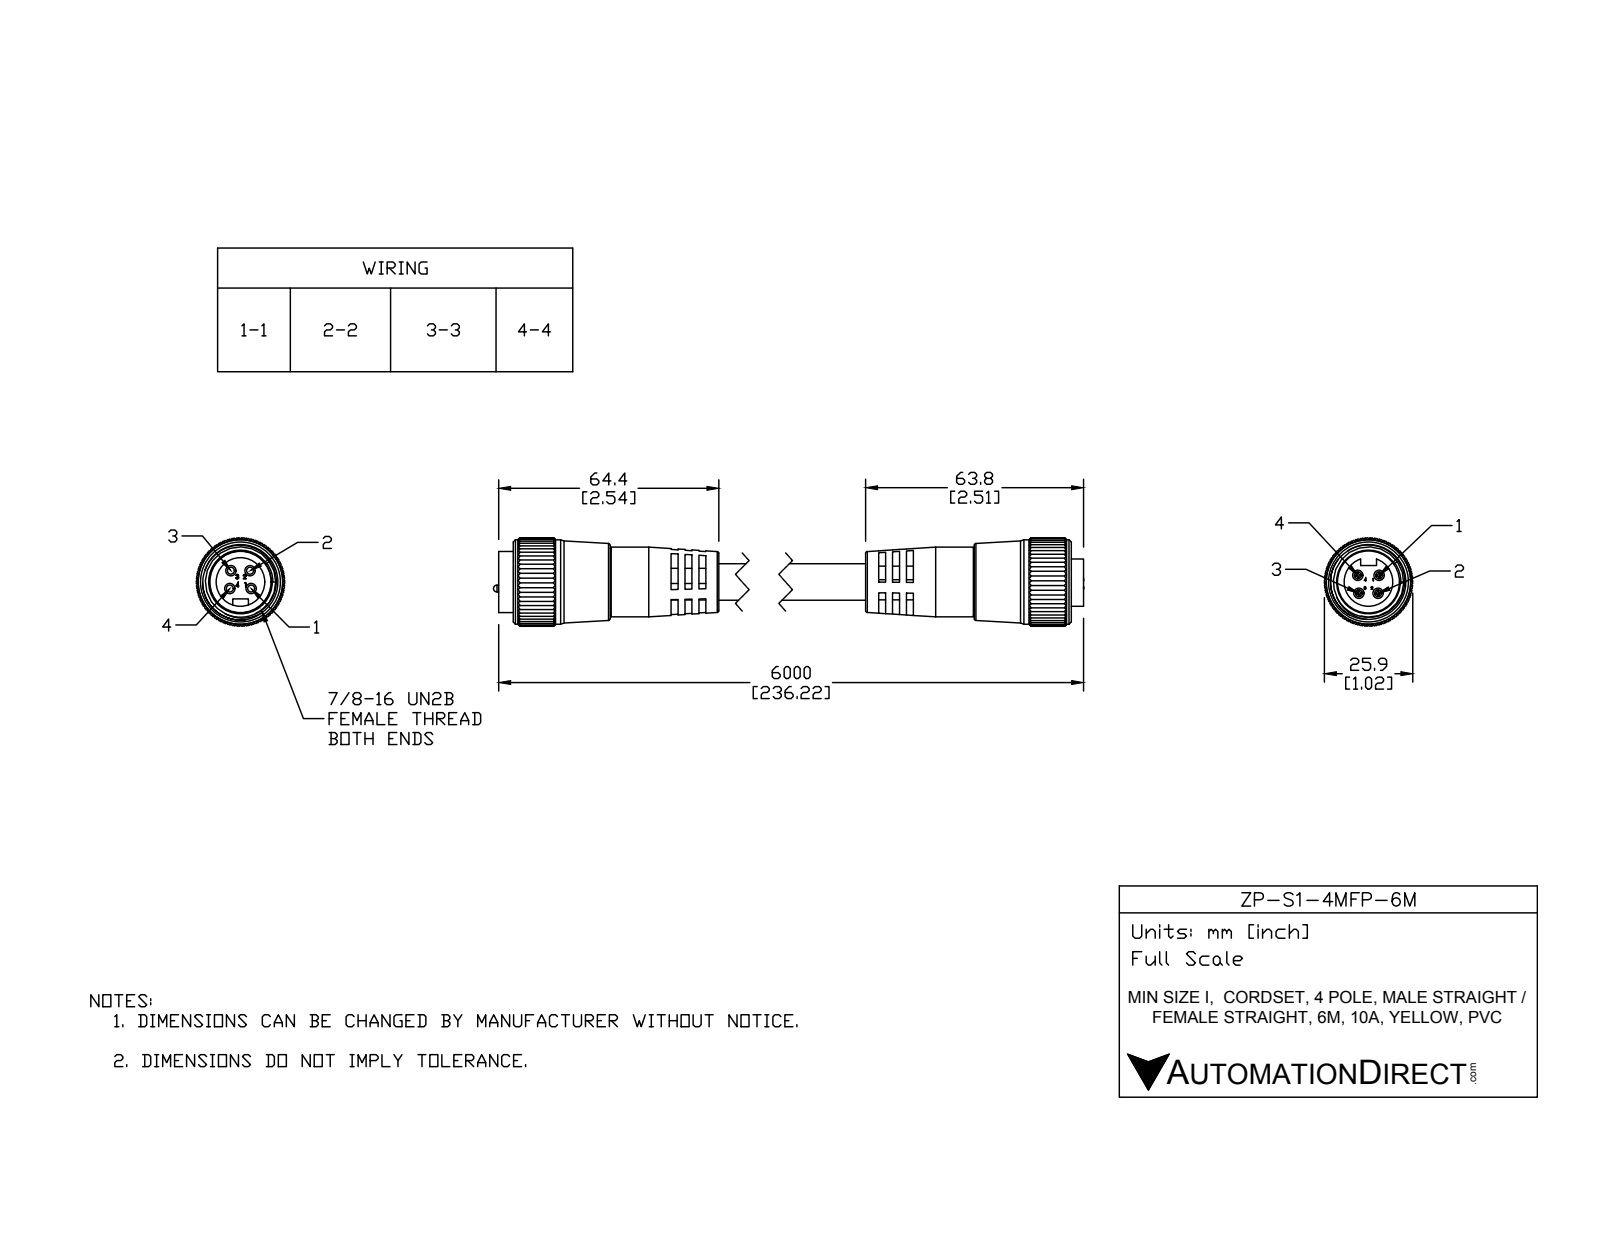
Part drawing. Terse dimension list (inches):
name: ZP-S1-4MFP-6M
written by: SolidWorks 2015 (AUTOMOTIVE_DESIGN)
unit: in
bodies: 8 solids, 1142 faces (422 planar, 624 cylindrical, 96 other)
size: 9.042 × 1.017 × 1.017
volume: 3.102 in³; area: 36.25 in²
holes: 4× ⌀0.12, 1× ⌀0.786, 1× ⌀0.805, 1× ⌀0.827
bosses: 4× ⌀0.12, 4× ⌀0.079, 1× ⌀0.972, 1× ⌀0.803, 1× ⌀0.768, 1× ⌀0.704, 1× ⌀0.56, 1× ⌀0.39
rounds: 165× R0.01, 1× R0.09, 1× R0.207, 1× R0.509
face distances: 0.079, 0.158, 4.633, 4.474, 0.159, 4.95, 2.356, 0.159, 4.791, 4.792
hole spacings: 0.144, 0.206, 0.17, 0.17, 0.22, 0.246, 0.311, 0.311
